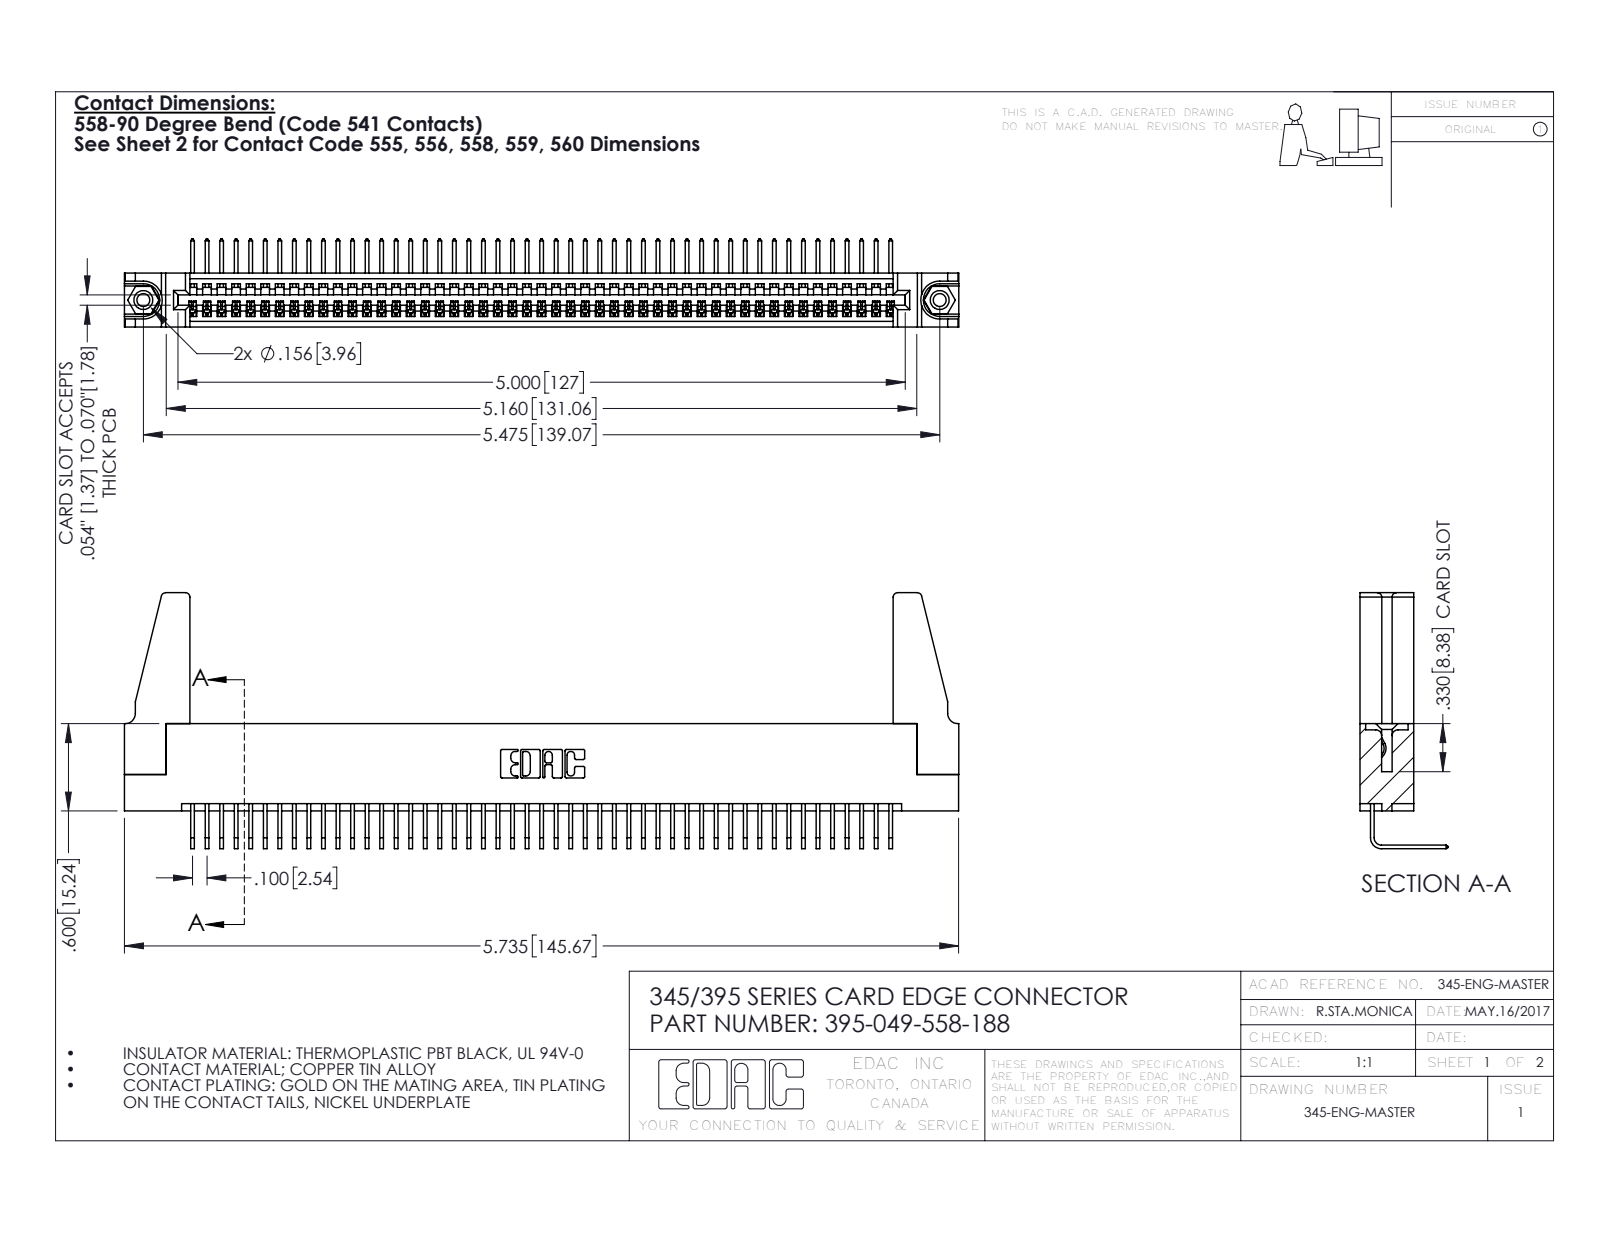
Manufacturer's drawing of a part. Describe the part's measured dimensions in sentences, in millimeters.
The part is named "395-049-558-188; 345-220-078_345-220-088; 345 Part_Flush Mounting Lugs - 0.156 Dia-TH; 345-250-001_345-250-001-102 (+1 more)". Its 3-D file was written by "SolidWorks 2016 (CONFIG_CONTROL_DESIGN)". It is 54 solids with 3190 faces: 2210 planar, 964 cylindrical and 16 other. Overall it measures 145.7 by 44.7 by 15.4 millimeters. Its volume is 17 300 cubic millimeters and its surface area 22 860 square millimeters. Round holes: 2 of diameter 2.3, 2 of diameter 3.2, 2 of diameter 4, 1 of diameter 1.6. Round bosses or shafts: 2 of diameter 3.9. Partial cylindrical surfaces (rounded edges, fillets, slot ends): 98 of radius 0.2, 22 of radius 0.3, 8 of radius 0.8, 6 of radius 0.2, 6 of radius 0.8, 3 of radius 0.7, 2 of radius 0.8, 2 of radius 1. The main face-to-face distances are 1.8, 7.6, 9.4, 5.1, 2.5, 6.9, 0.6, 5.7, 3.8, 1.8. The hole center spacings are 6.9, 133.1, 139.1.
